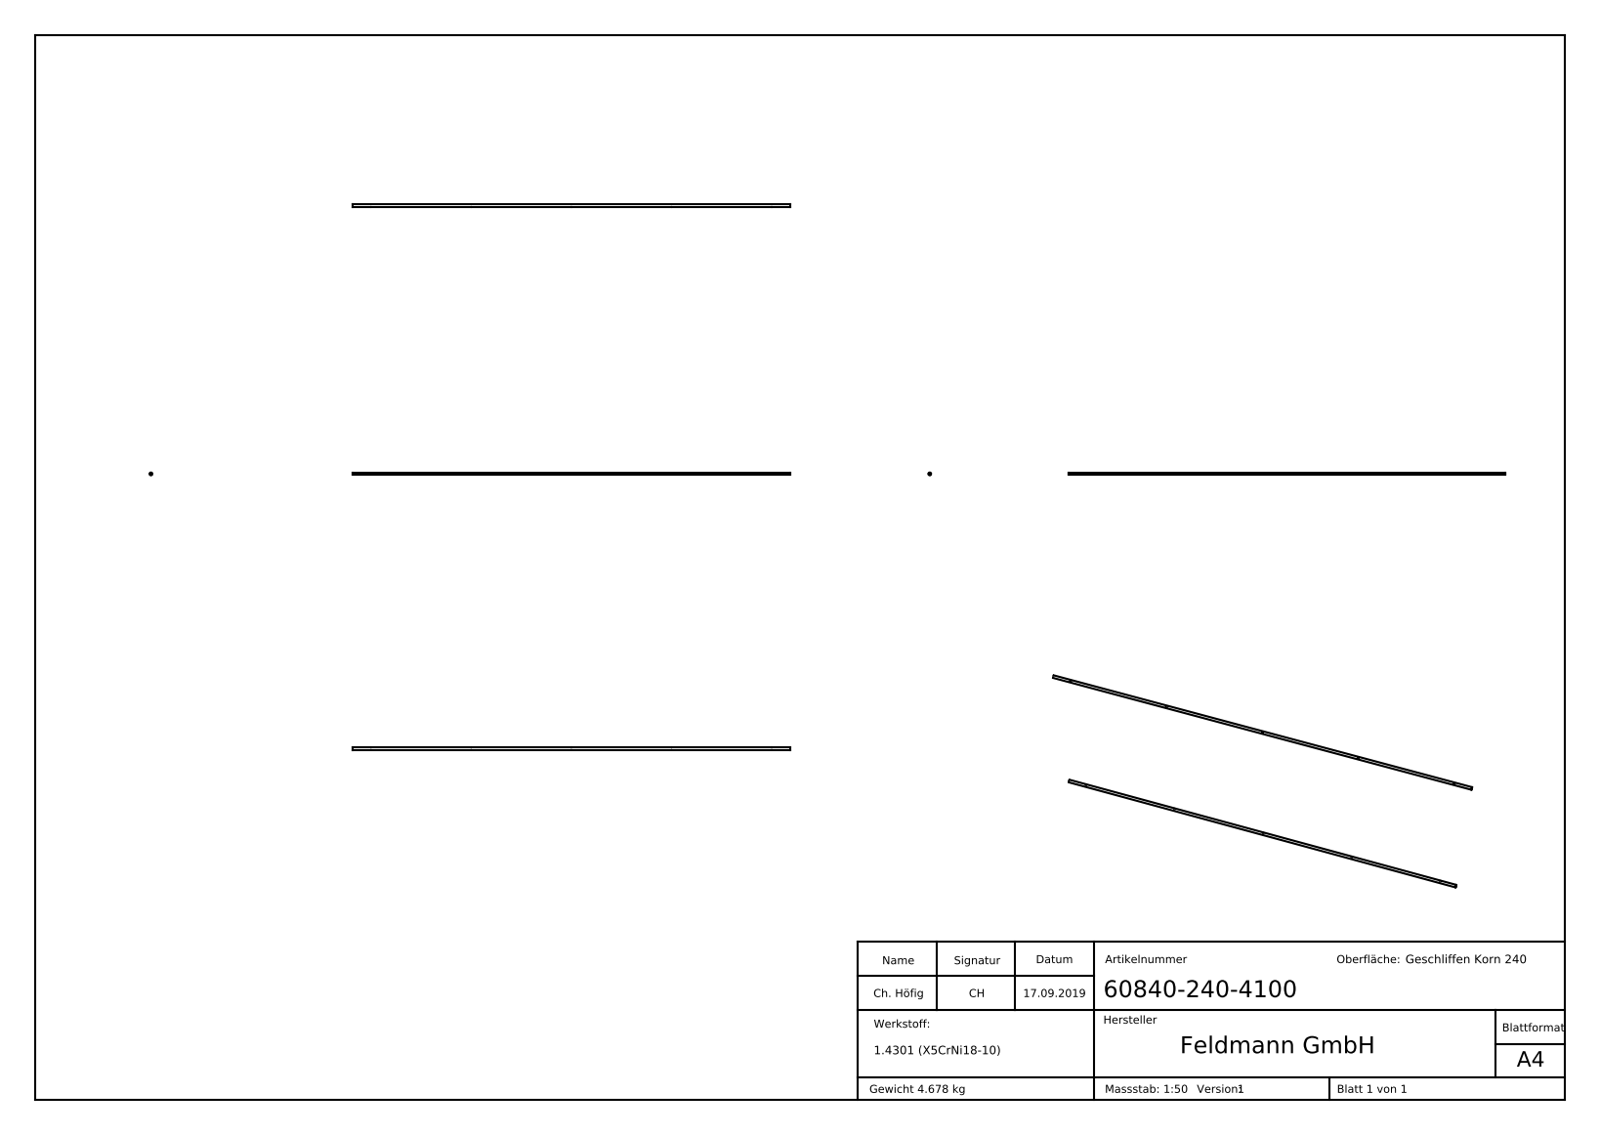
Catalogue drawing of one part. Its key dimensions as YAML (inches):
part_name: "60840-240-4100"
step_written_by: "SolidWorks 2015 (CONFIG_CONTROL_DESIGN)"
units: inches
bodies: {solids: 1, faces: 302, planar: 118, cylindrical: 59, other: 125}
overall_size: [161.417, 0.984, 0.984]
volume: 36.13
surface_area: 918.6
round_holes:
  - {diameter: 0.268, count: 5}
  - {diameter: 0.827, count: 1}
round_bosses_or_shafts:
  - {diameter: 0.984, count: 1}
partial_cylinders:
  - {radius: 0.417, count: 1}
face_to_face_distances: [161.417, 0.129, 0.331, 0.109, 0.031, 0.135, 0.28, 0.104, 0.248, 0.144]
hole_center_spacings: [37.008, 74.016, 111.024, 148.031]
